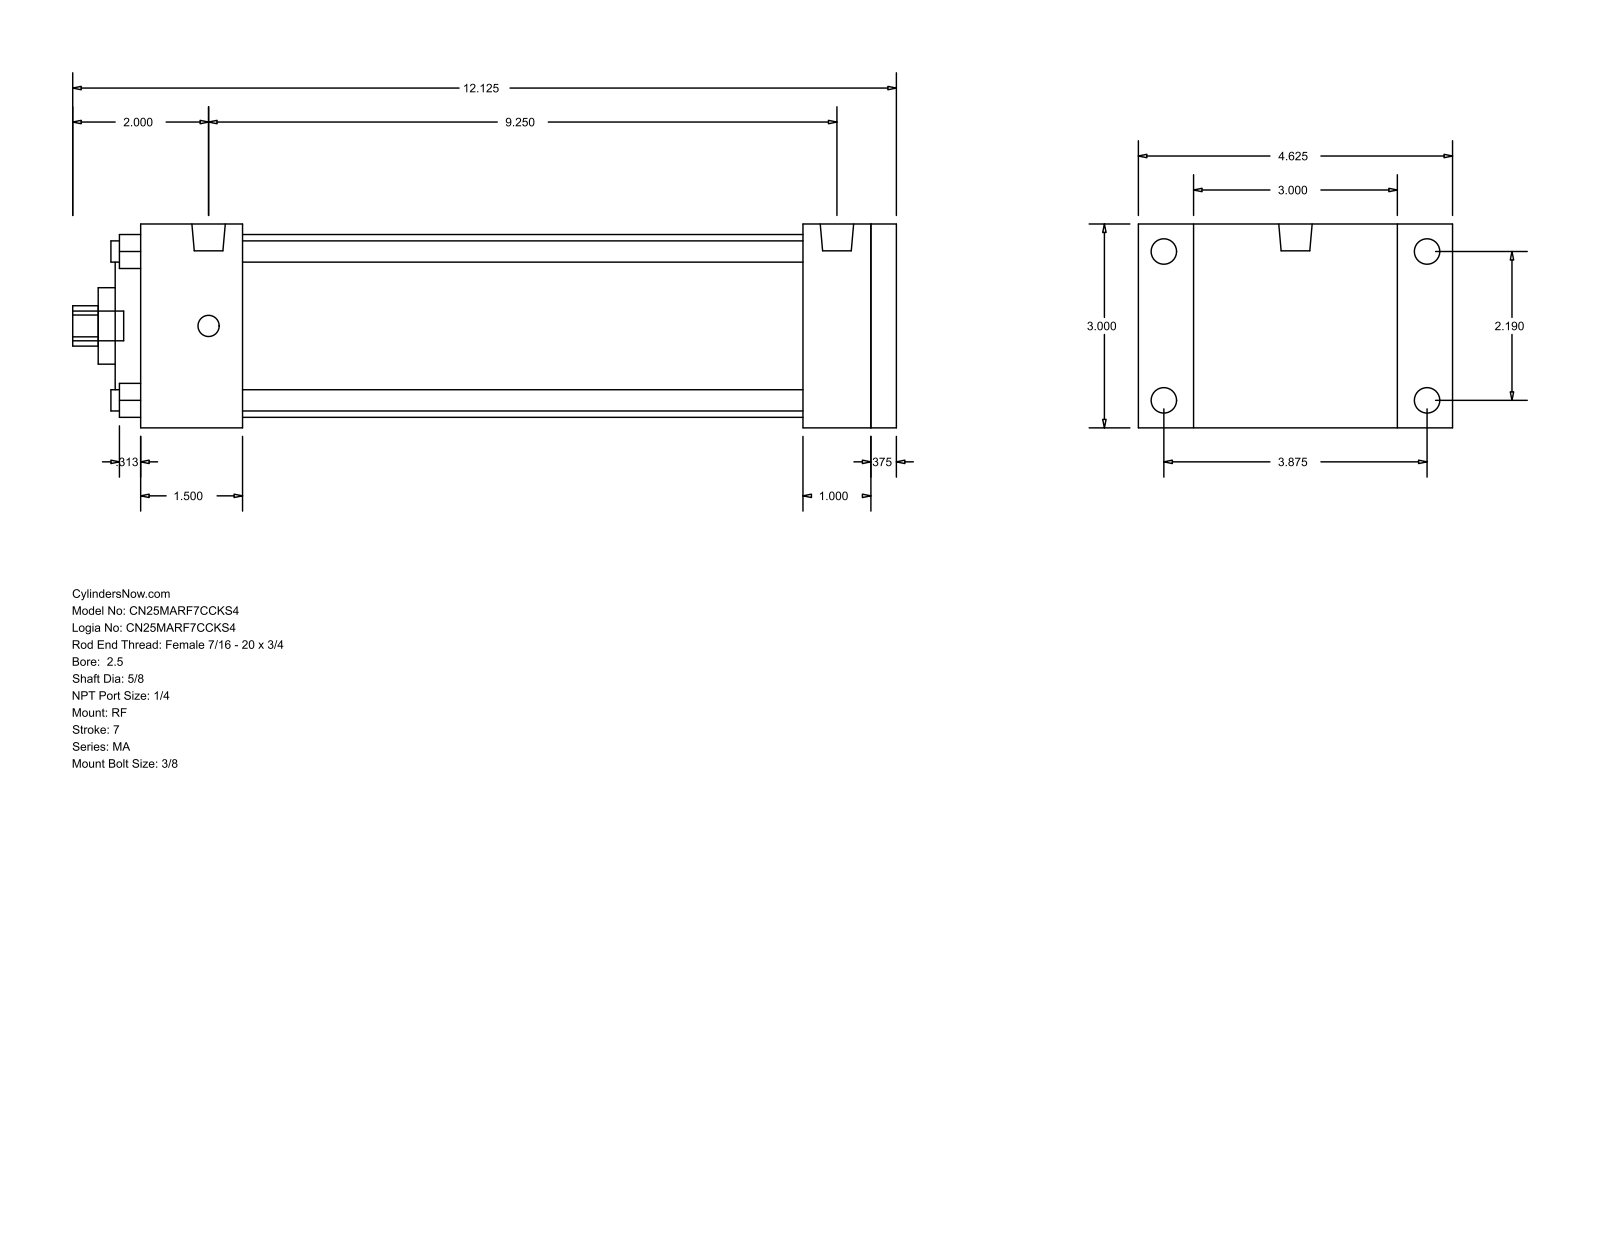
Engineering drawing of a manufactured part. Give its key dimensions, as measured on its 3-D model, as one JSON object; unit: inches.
{"part_name": "MA_RF__0250_0.625", "step_written_by": "GSSL Pune (CONFIG_CONTROL_DESIGN)", "units": "inches", "bodies": {"solids": 0, "faces": 94, "planar": 65, "cylindrical": 29, "other": 0}, "overall_size": [12.125, 4.625, 3], "round_holes": [[0.313, 4], [0.625, 1], [1.125, 1], [2, 1], [2.69, 1]], "round_bosses_or_shafts": [[0.375, 4], [0.313, 4], [0.492, 2], [0.437, 1]], "partial_cylinders_radius": [[0.297, 1]], "face_to_face_distances": [3, 11.125, 0.375, 10.75, 1, 1.5, 9.75, 8.25, 9.25, 9.625], "hole_center_spacings": [1.548, 2.19, 3.097]}
